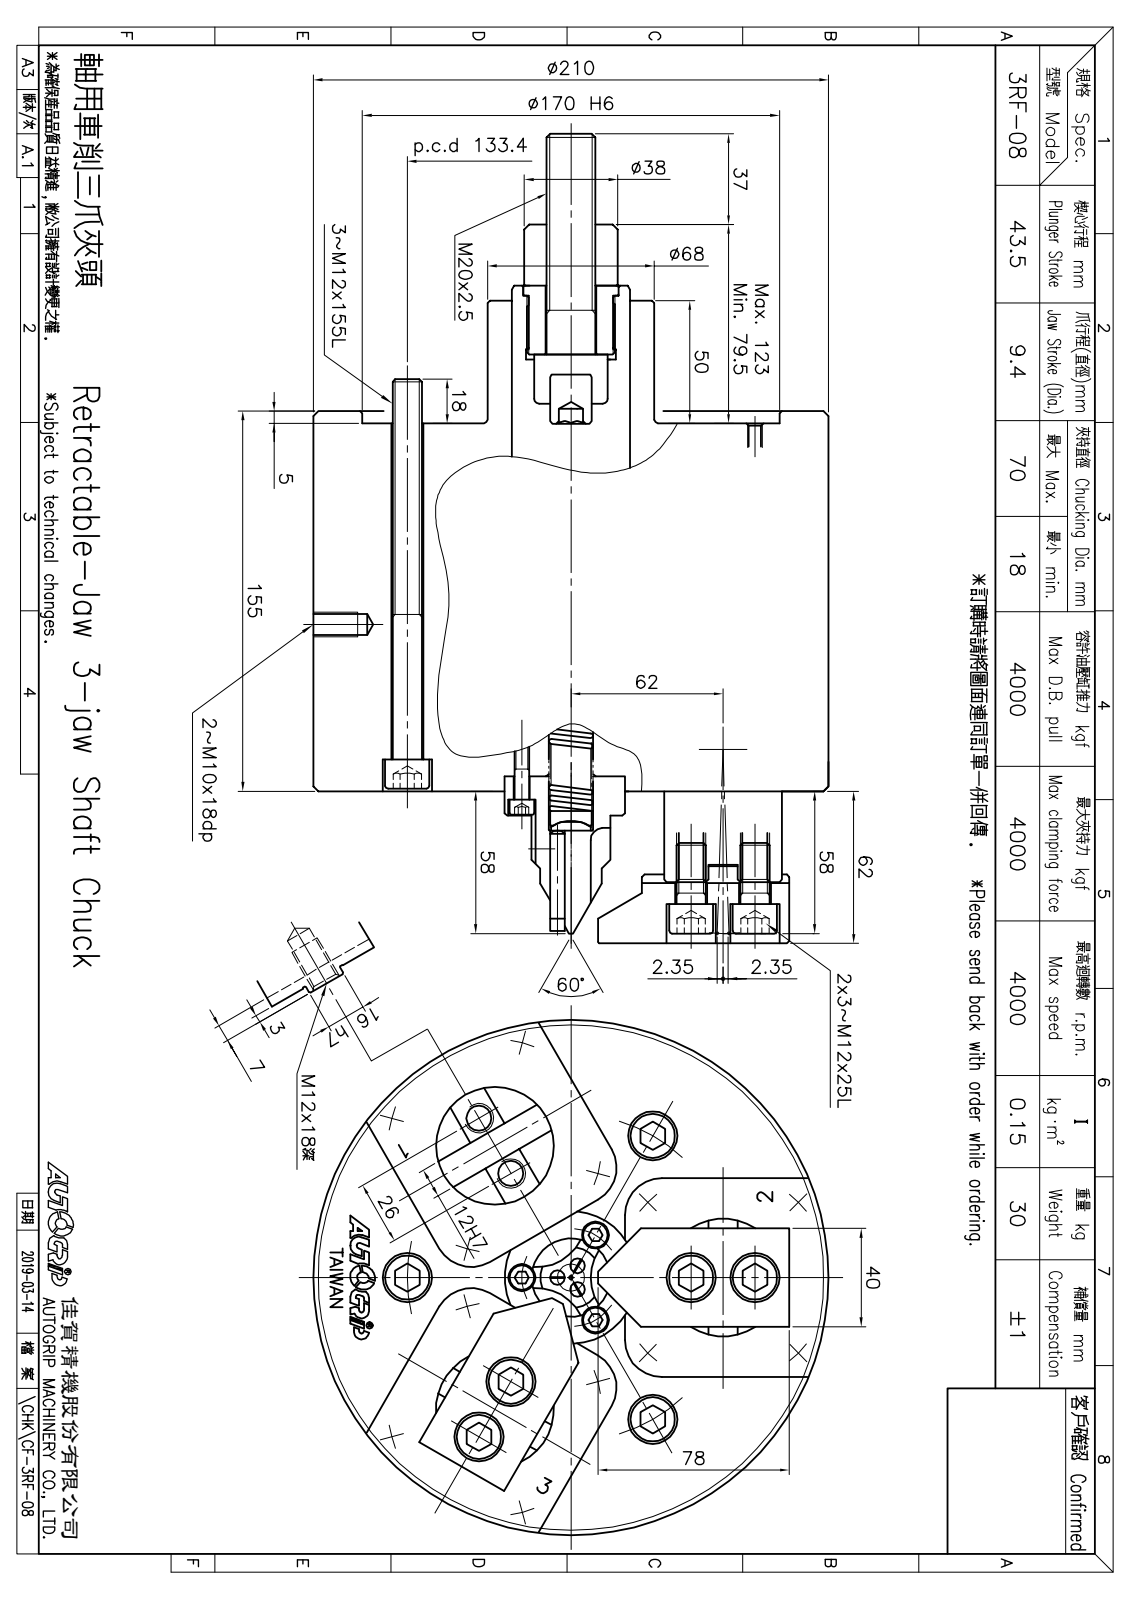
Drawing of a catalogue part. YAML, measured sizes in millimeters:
part_name: "CF-3RF-08-03000; 圓頭內六角螺栓_M12x25; CF-3RF-08-20000; CF-3RF-08-13000 (+8 more)"
step_written_by: "SolidWorks 2020 (CONFIG_CONTROL_DESIGN)"
units: millimeters
bodies: {solids: 45, faces: 1629, planar: 776, cylindrical: 406, other: 447}
overall_size: [333.62, 210, 210]
volume: 4672000
surface_area: 624120
round_holes:
  - {diameter: 5, count: 12}
  - {diameter: 6.6, count: 12}
  - {diameter: 11, count: 12}
  - {diameter: 13, count: 9}
  - {diameter: 20, count: 9}
  - {diameter: 6.8, count: 7}
  - {diameter: 10.2, count: 6}
  - {diameter: 48, count: 4}
  - {diameter: 6, count: 3}
  - {diameter: 9, count: 3}
  - {diameter: 13.5, count: 3}
  - {diameter: 14, count: 3}
round_bosses_or_shafts:
  - {diameter: 10, count: 12}
  - {diameter: 6, count: 12}
  - {diameter: 18, count: 9}
  - {diameter: 12, count: 9}
  - {diameter: 8, count: 4}
  - {diameter: 50, count: 3}
  - {diameter: 47.5, count: 3}
  - {diameter: 46, count: 3}
partial_cylinders:
  - {radius: 0.4, count: 6}
  - {radius: 15, count: 6}
  - {radius: 20, count: 3}
  - {radius: 12, count: 1}
  - {radius: 30, count: 1}
face_to_face_distances: [130, 12, 150, 20, 138, 118, 5, 88, 143, 30]
hole_center_spacings: [43.5, 61.52, 93.69, 38.57, 43.84, 53.16, 59.44, 64.48]
